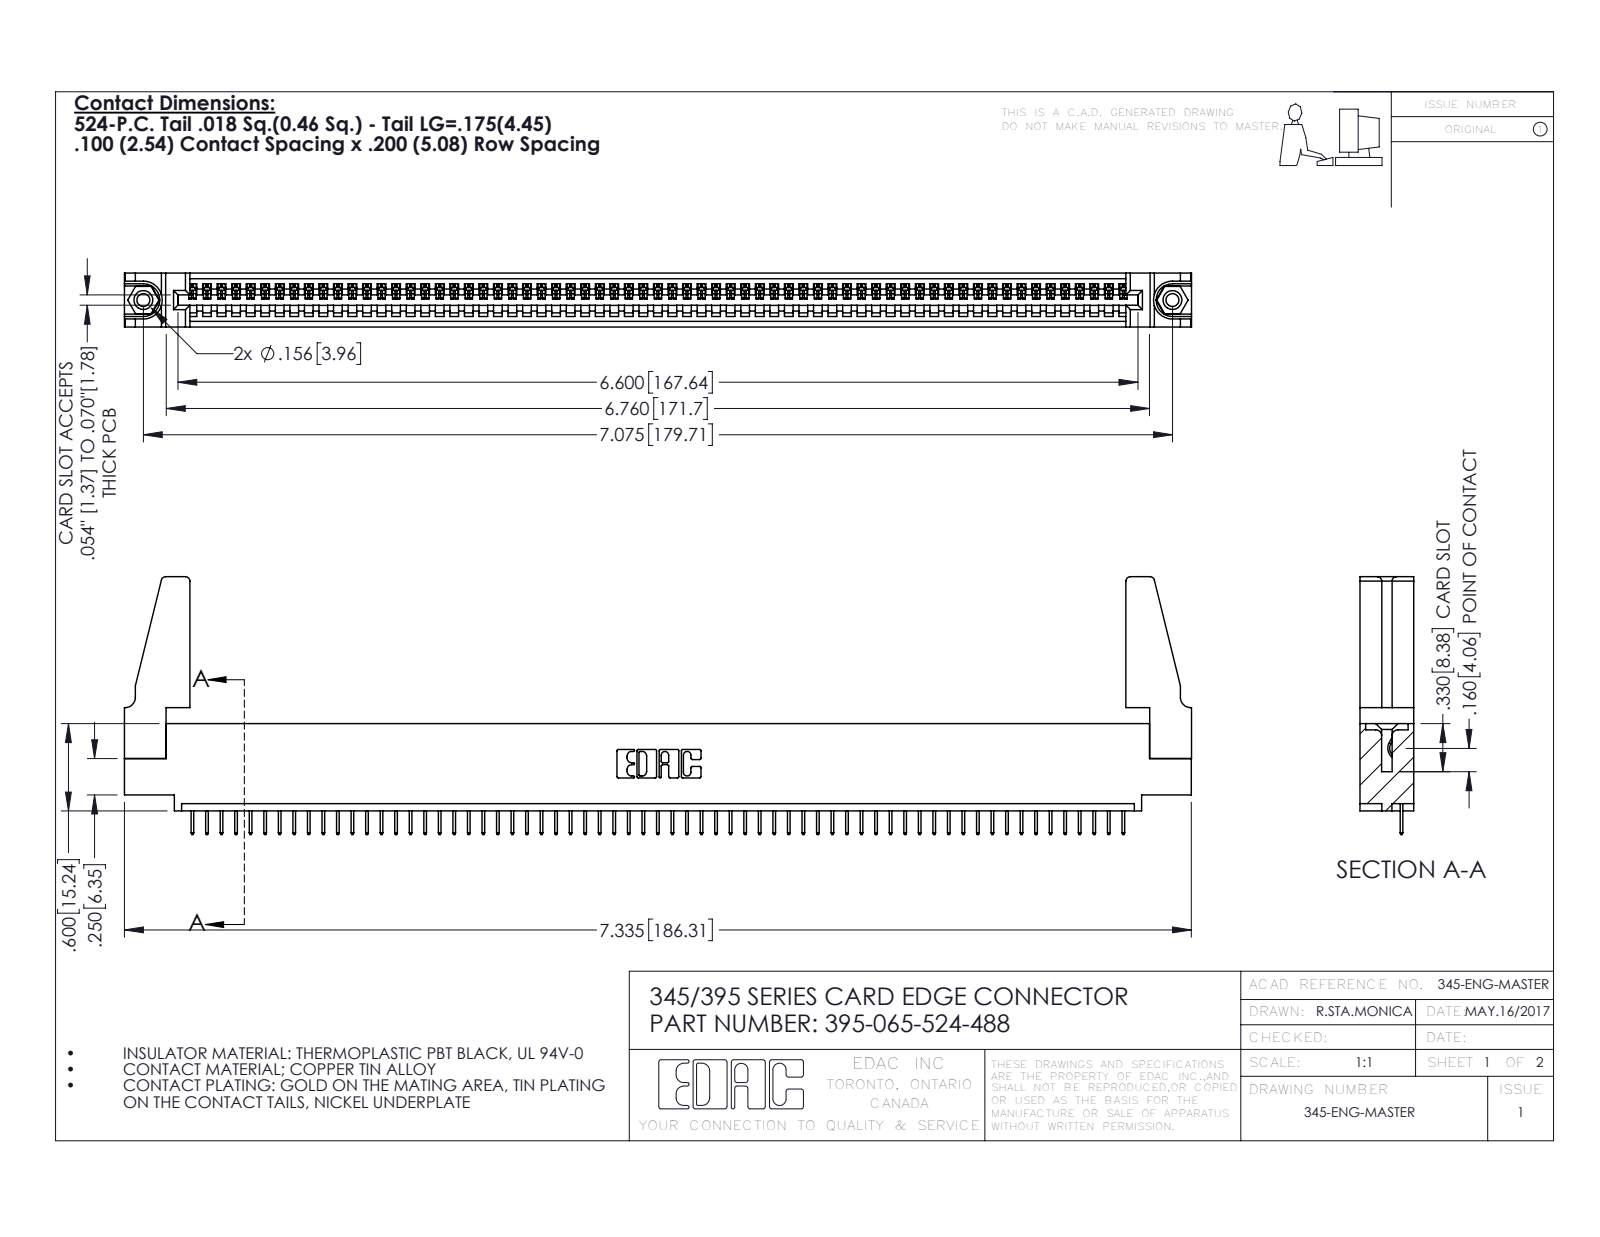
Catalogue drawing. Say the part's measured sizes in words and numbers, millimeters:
The part is named "345-250-001_345-250-001-102; 345-292-001_345-293-124; 395-065-524-488; 345-220-078_345-220-088 (+1 more)". Its 3-D file was written by "SolidWorks 2016 (CONFIG_CONTROL_DESIGN)". It is 70 solids with 4284 faces: 3146 planar, 1122 cylindrical and 16 other. Overall it measures 186.3 by 45 by 9.4 millimeters. Its volume is 20 810 cubic millimeters and its surface area 26 030 square millimeters. Round holes: 2 of diameter 2.3, 2 of diameter 3.2, 2 of diameter 4, 1 of diameter 1.6. Round bosses or shafts: 2 of diameter 3.9. Partial cylindrical surfaces (rounded edges, fillets, slot ends): 130 of radius 0.2, 22 of radius 0.3, 8 of radius 0.8, 6 of radius 0.2, 6 of radius 0.8, 3 of radius 0.7, 2 of radius 0.8, 2 of radius 1. The main face-to-face distances are 1.8, 7.6, 9.4, 5.1, 2.5, 6.9, 0.6, 5.7, 1.8, 3.8. The hole center spacings are 6.9, 173.7, 179.7.
